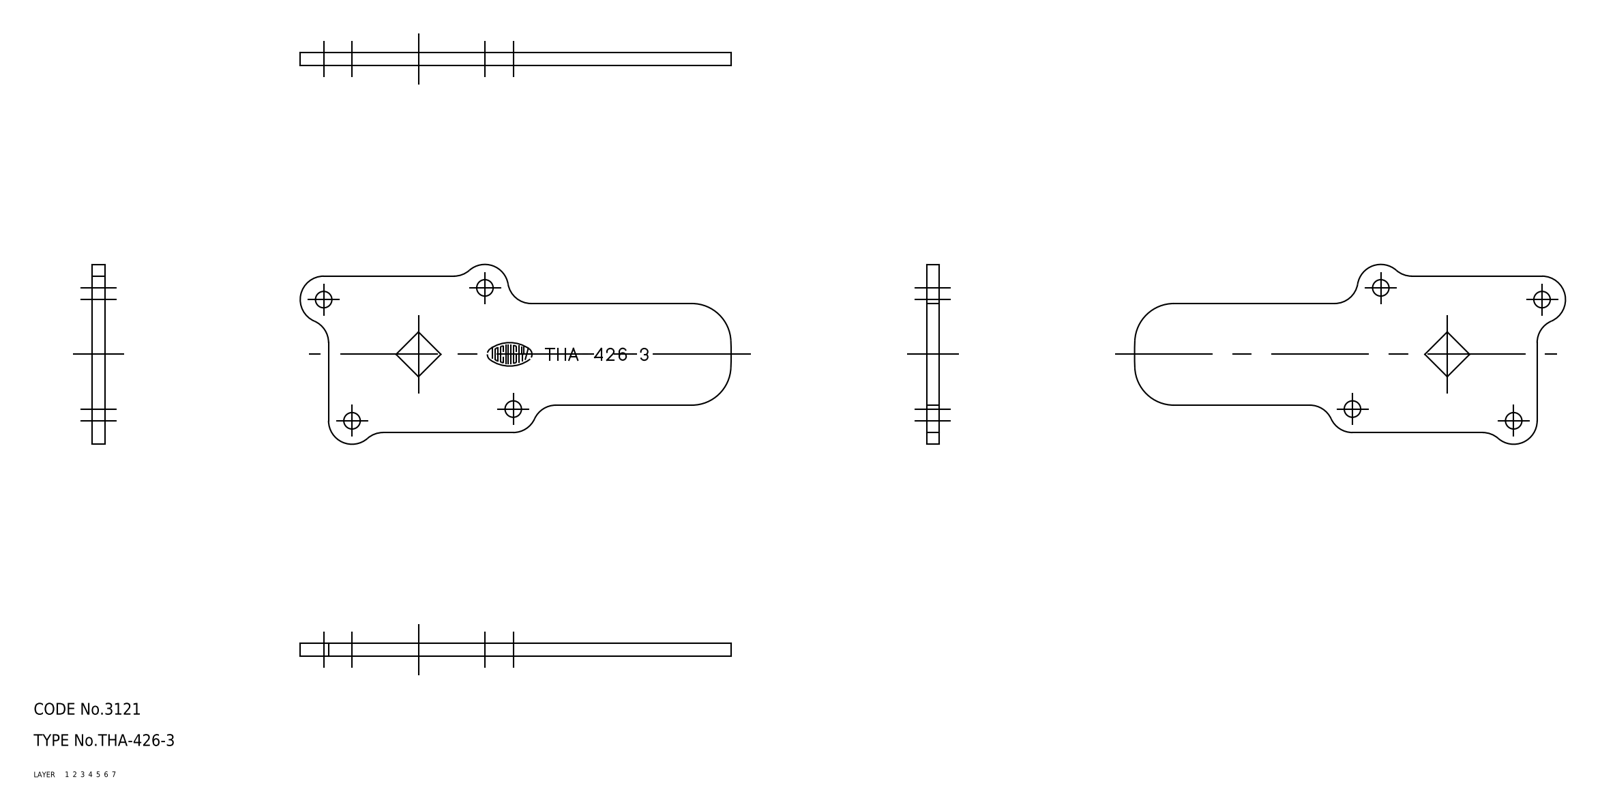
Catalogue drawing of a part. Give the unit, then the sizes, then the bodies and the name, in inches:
Units: inches
Overall size (bounding box): 4.341 × 1.811 × 0.126
Volume: 0.65 in³ · Surface area: 12.14 in²
Bodies: 1 solid, 31 faces (0 planar, 0 cylindrical, 31 other)
Part name (STEP PRODUCT): cam
STEP written by: CADfix (AUTOMOTIVE_DESIGN)
